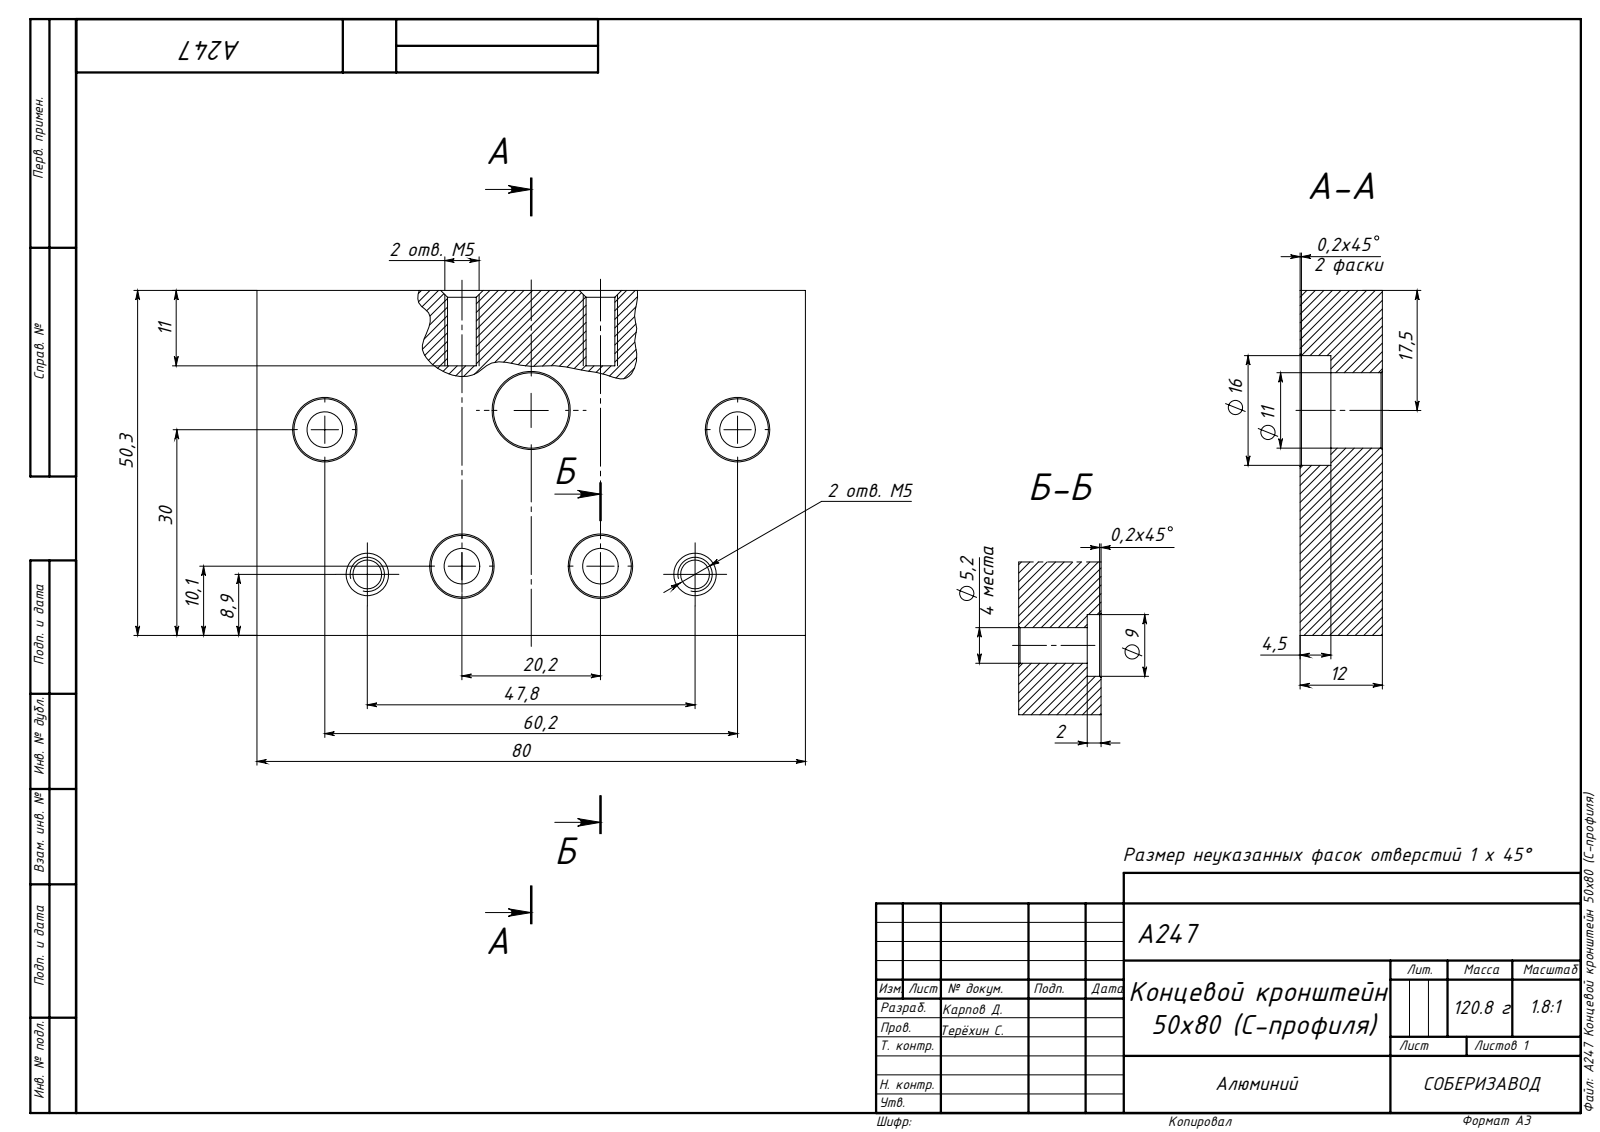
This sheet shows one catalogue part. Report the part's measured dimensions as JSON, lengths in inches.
{"part_name": "A247 Концевой кронштейн 50х80 (С-профиля)", "step_written_by": "SolidWorks 2018 (AUTOMOTIVE_DESIGN)", "units": "inches", "bodies": {"solids": 1, "faces": 73, "planar": 13, "cylindrical": 28, "other": 32}, "overall_size": [3.15, 1.98, 0.472], "volume_in3": 2.723, "surface_area_in2": 19.63, "round_holes": [[0.165, 4], [0.205, 4], [0.354, 4], [0.433, 1], [0.63, 1]], "face_to_face_distances": [0.472, 1.98, 3.15, 0.079, 0.394, 0.295, 0.217, 0.177, 1.547, 0.433], "hole_center_spacings": [0.545, 0.795, 0.866, 0.978, 1.111, 1.19, 1.331, 1.339]}
